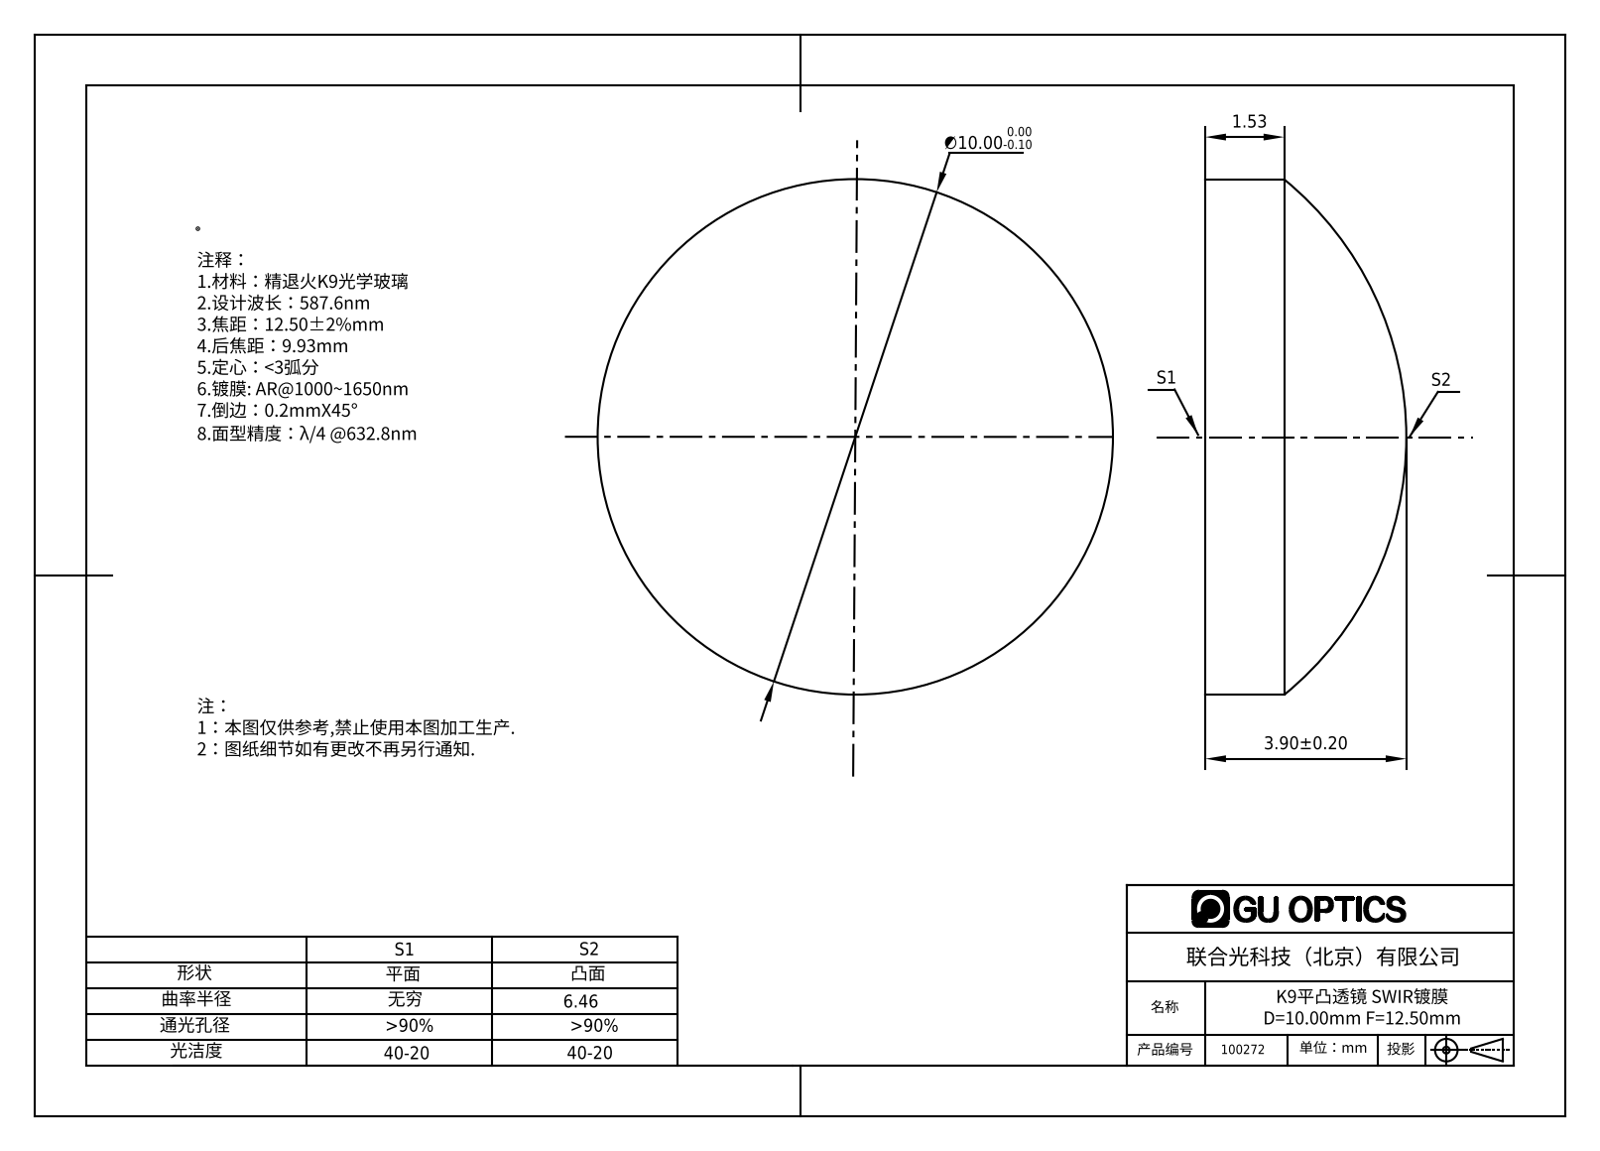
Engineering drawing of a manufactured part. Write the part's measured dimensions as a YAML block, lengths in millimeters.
part_name: "100100"
step_written_by: "SolidWorks 2016 (AUTOMOTIVE_DESIGN)"
units: millimeters
bodies: {solids: 1, faces: 5, planar: 1, cylindrical: 2, other: 2}
overall_size: [10, 10, 3.9]
volume: 220
surface_area: 223
round_bosses_or_shafts:
  - {diameter: 10, count: 1}
